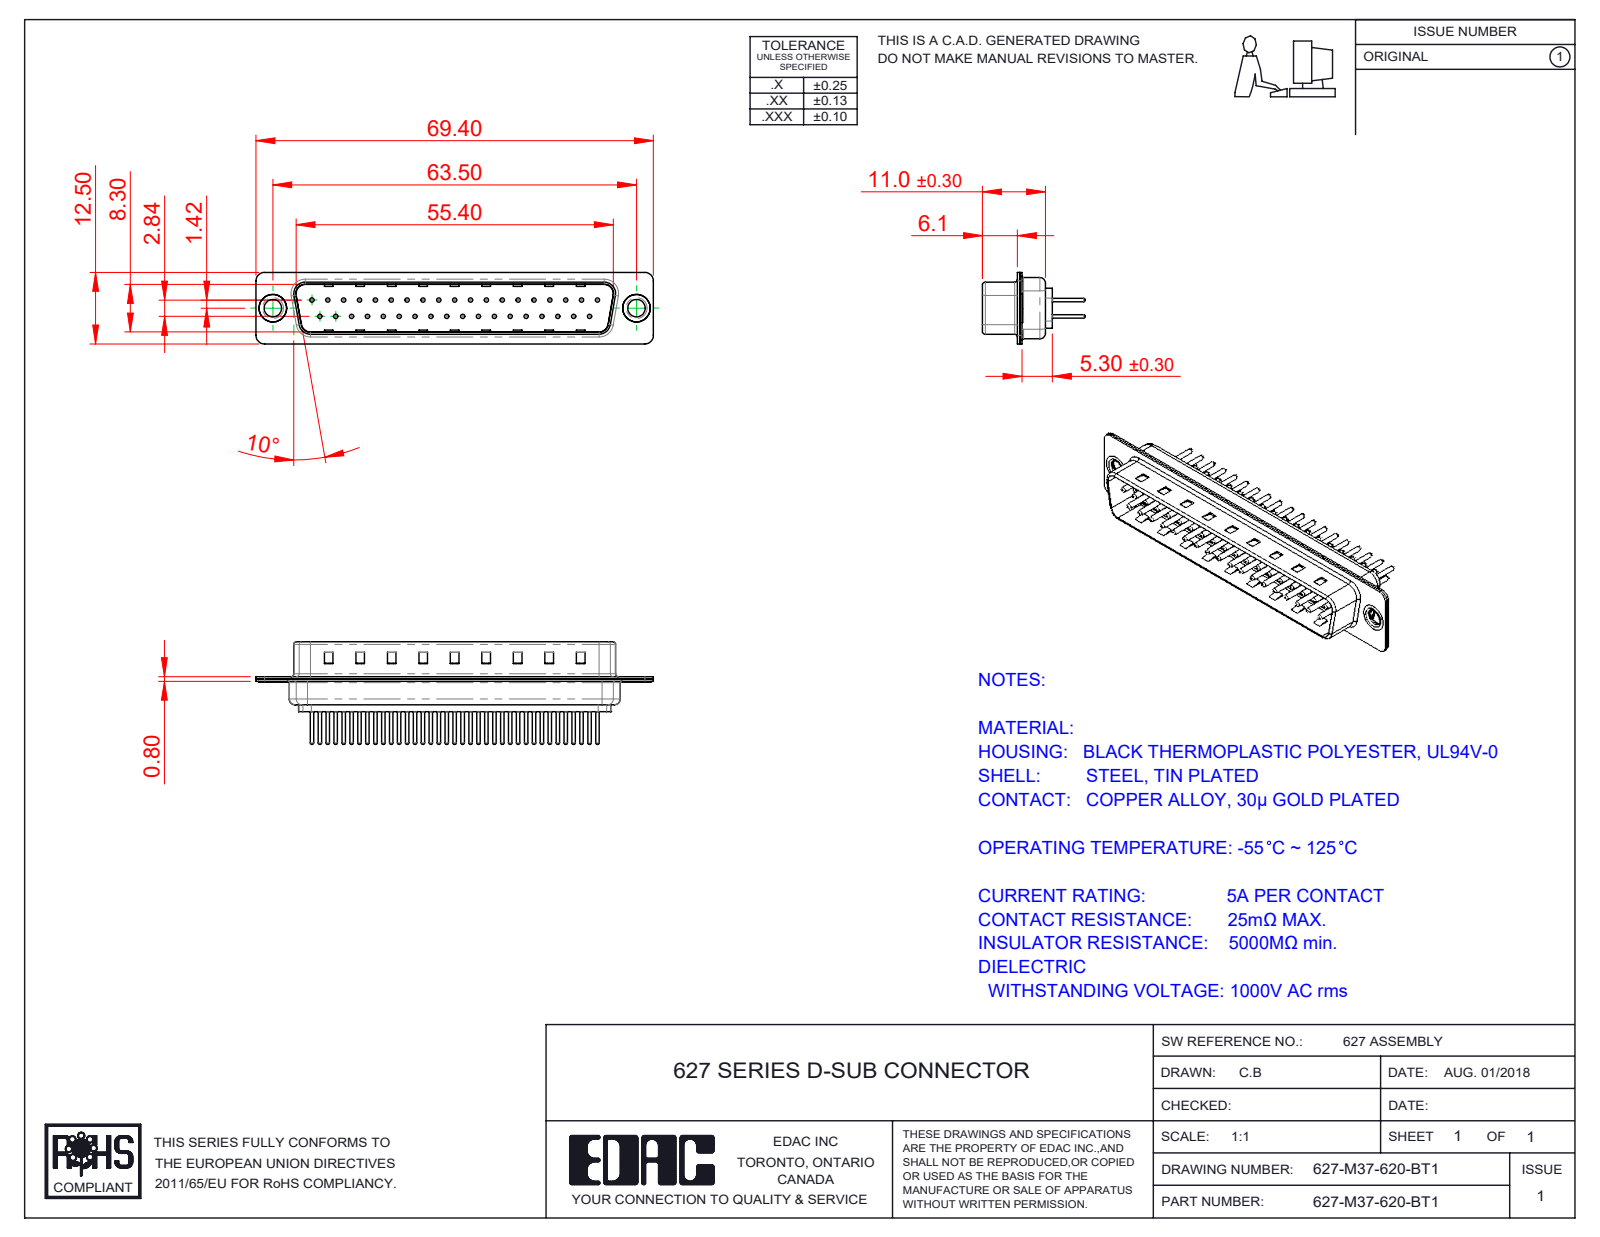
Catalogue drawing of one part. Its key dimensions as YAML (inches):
part_name: "627M Contact Row 2_20; 627M Shell Front_37 Contacts; 627M Housing_37 Contacts; 627M Shell Rear_37 Contacts (+3 more)"
step_written_by: "SolidWorks 2020 (CONFIG_CONTROL_DESIGN)"
units: inches
bodies: {solids: 42, faces: 1755, planar: 462, cylindrical: 643, other: 650}
overall_size: [2.732, 0.705, 0.492]
volume: 0.225
surface_area: 14.14
round_holes:
  - {diameter: 0.03, count: 37}
  - {diameter: 0.063, count: 37}
  - {diameter: 0.079, count: 37}
  - {diameter: 0.12, count: 2}
  - {diameter: 0.157, count: 2}
  - {diameter: 0.189, count: 2}
round_bosses_or_shafts:
  - {diameter: 0.059, count: 37}
  - {diameter: 0.024, count: 37}
  - {diameter: 0.197, count: 2}
  - {diameter: 0.193, count: 2}
  - {diameter: 0.14, count: 2}
partial_cylinders:
  - {radius: 0.059, count: 16}
  - {radius: 0.079, count: 12}
  - {radius: 0.02, count: 8}
  - {radius: 0.063, count: 8}
  - {radius: 0.01, count: 4}
  - {radius: 0.024, count: 4}
  - {radius: 0.026, count: 4}
  - {radius: 0.035, count: 4}
face_to_face_distances: [0.016, 0.031, 0.374, 0.358, 0.343, 0.39, 0.047, 0.224, 0.03, 0.014]
hole_center_spacings: [0.109, 0.218, 0.124, 0.327, 0.436, 0.545, 0.654, 0.763]
